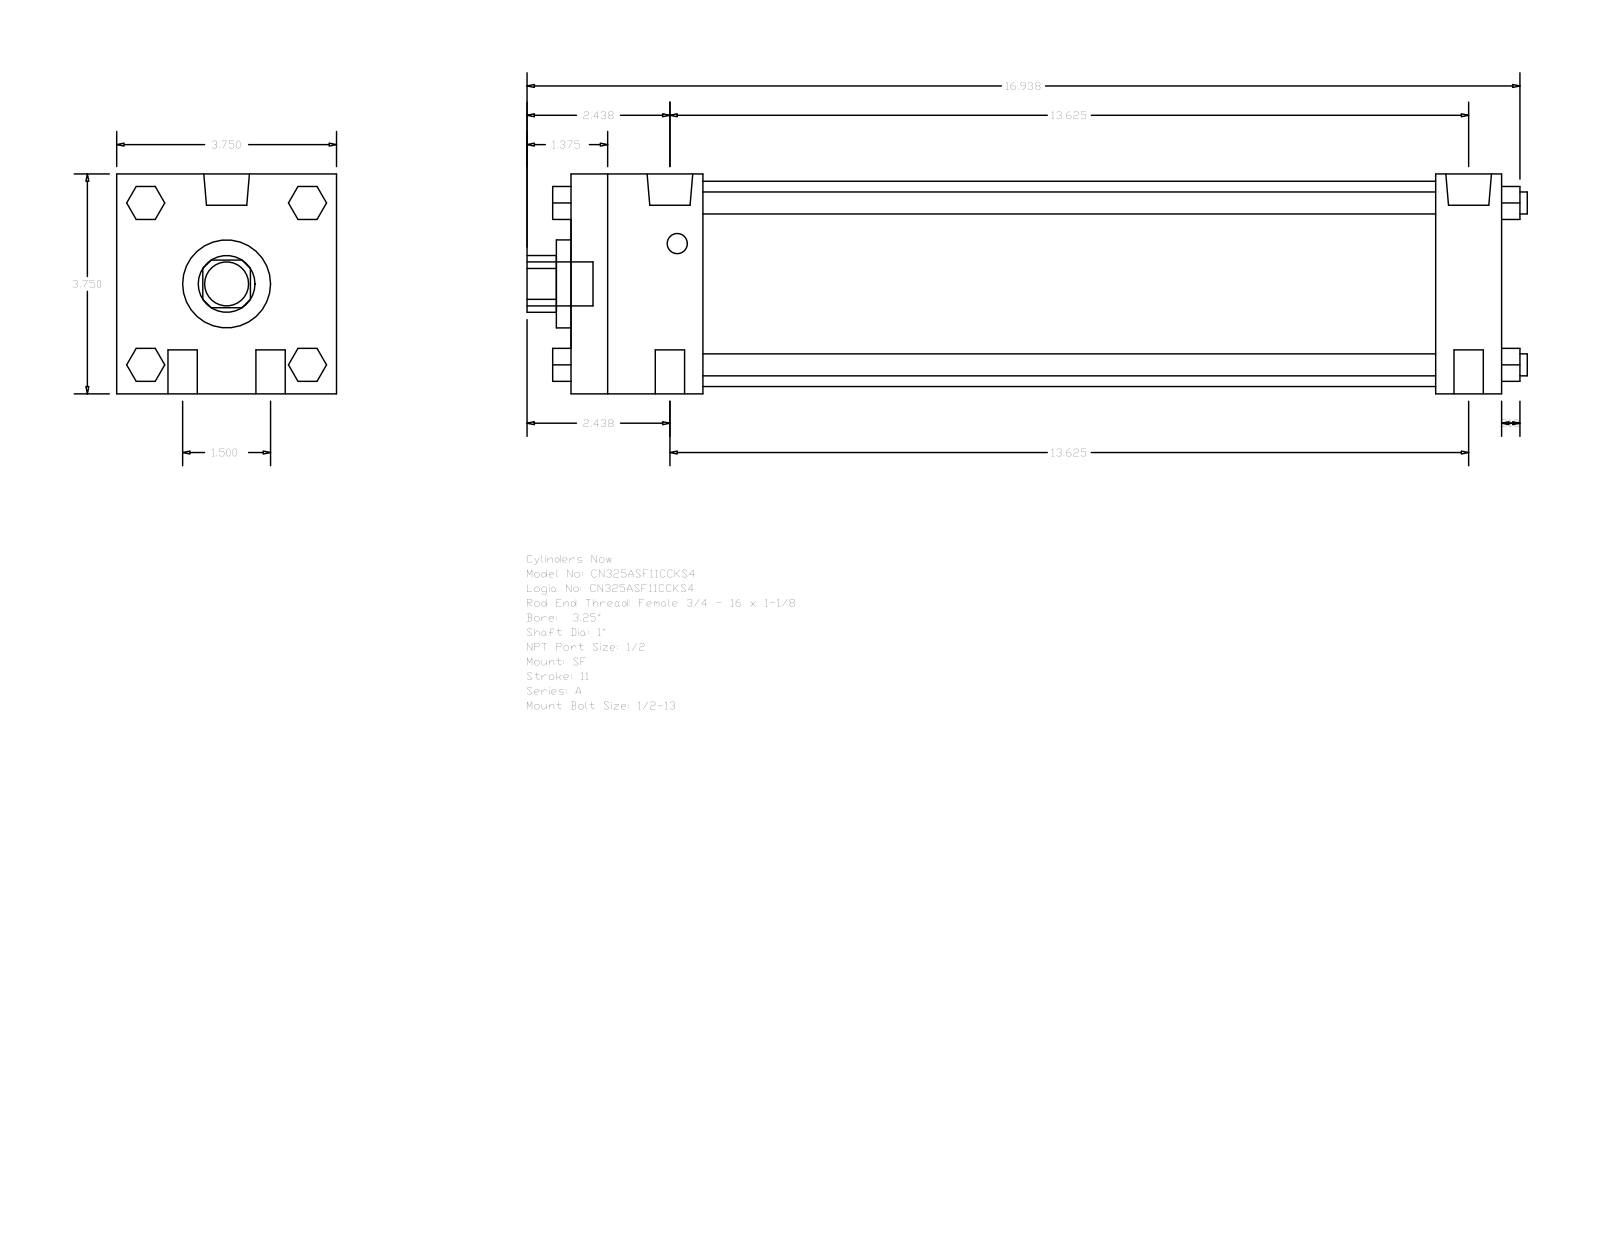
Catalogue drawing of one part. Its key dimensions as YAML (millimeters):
part_name: "A_SF__0325_1"
step_written_by: "GSSL Pune (CONFIG_CONTROL_DESIGN)"
units: millimeters
bodies: {solids: 0, faces: 124, planar: 94, cylindrical: 30, other: 0}
overall_size: [433.39, 95.25, 95.25]
round_holes:
  - {diameter: 25.4, count: 1}
  - {diameter: 38.1, count: 1}
  - {diameter: 88.9, count: 1}
round_bosses_or_shafts:
  - {diameter: 12.7, count: 4}
  - {diameter: 9.53, count: 4}
  - {diameter: 19.77, count: 2}
  - {diameter: 8.73, count: 2}
  - {diameter: 19.05, count: 1}
partial_cylinders:
  - {radius: 12.29, count: 1}
face_to_face_distances: [95.24, 403.22, 28.57, 374.65, 57.15, 317.5, 346.07, 14.28, 35.05, 60.71]
